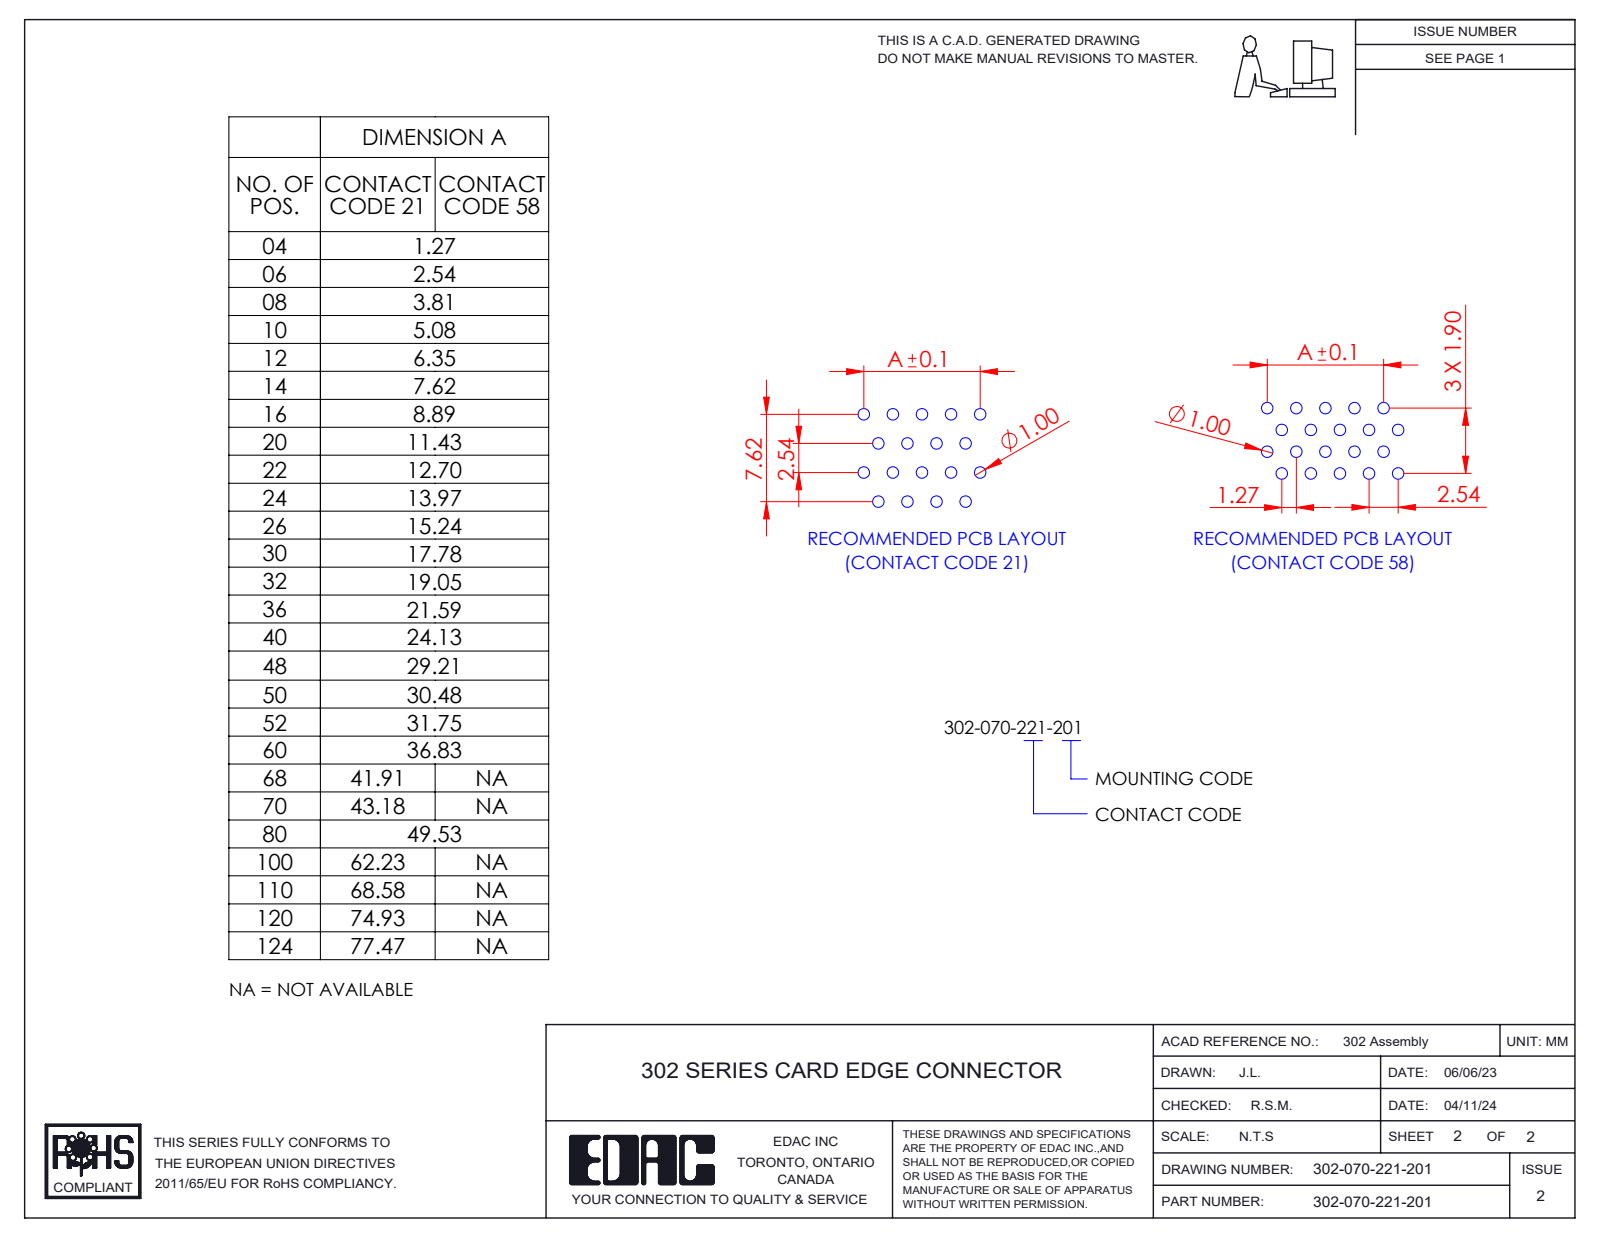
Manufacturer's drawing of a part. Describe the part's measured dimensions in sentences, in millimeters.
The part is named "HSG_Vertical HSG; Contact_302-290-X21 (2); Contact_302-290-X21 (1); 302-070-221-201". Its 3-D file was written by "SolidWorks 2023 (CONFIG_CONTROL_DESIGN)". It is 71 solids with 3251 faces: 2394 planar, 713 cylindrical and 144 other. Overall it measures 50.55 by 17.63 by 8.88 millimeters. Its volume is 3 929 cubic millimeters and its surface area 10 748 square millimeters. Partial cylindrical surfaces (rounded edges, fillets, slot ends): 78 of radius 0.2, 4 of radius 2.03, 4 of radius 2.09, 2 of radius 0.11, 2 of radius 0.4, 2 of radius 0.41, 2 of radius 1.25, 2 of radius 1.53. The main face-to-face distances are 2.54, 1.27, 5.08, 3.81, 7.62, 6.35, 8.88, 8.89, 10.16, 11.43.
